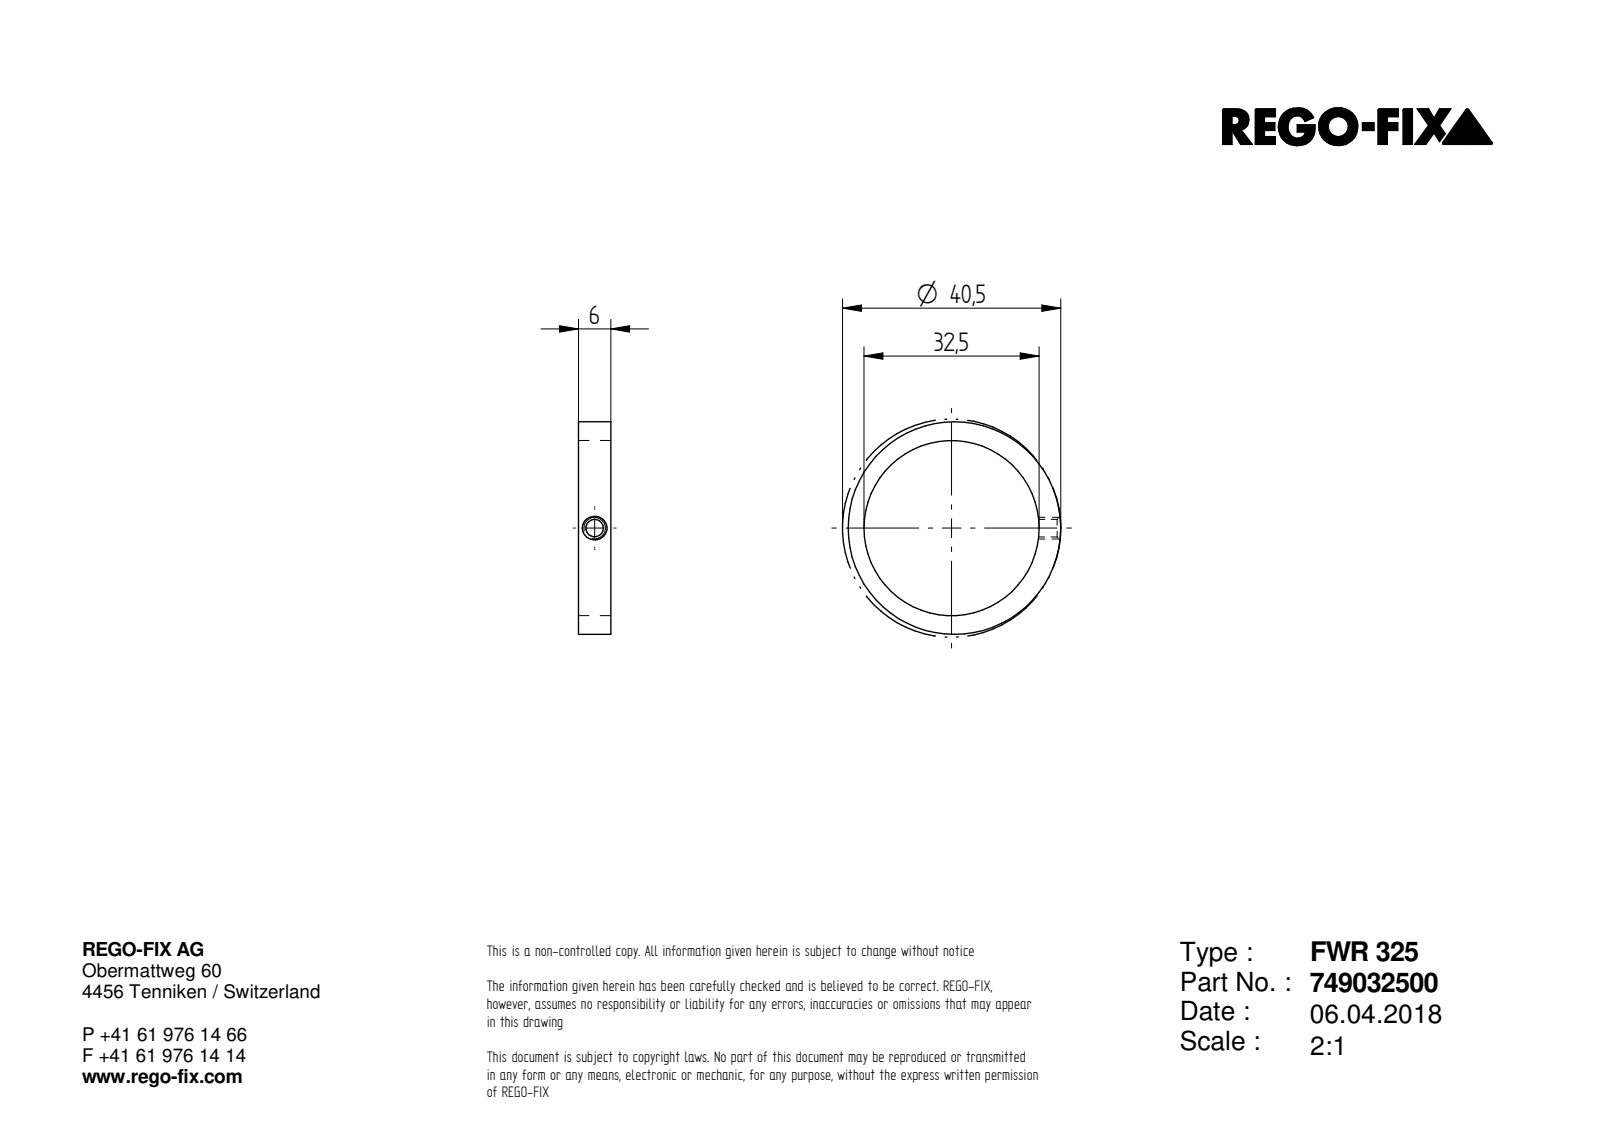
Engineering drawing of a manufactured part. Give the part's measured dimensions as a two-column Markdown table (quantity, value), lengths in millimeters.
| quantity | value |
| --- | --- |
| STEP written by | Unknown (AUTOMOTIVE_DESIGN) |
| units | millimeters |
| bodies | 1 solid, 6 faces (2 planar, 3 cylindrical, 1 other) |
| overall size | 39.45 × 39.45 × 6 |
| volume | 2 321 mm³ |
| surface area | 2 162 mm² |
| round holes (diameter × count) | 3.24 × 1, 32.5 × 1 |
| round bosses / shafts (diameter × count) | 39.45 × 1 |
| main face-to-face distances | 6 |
